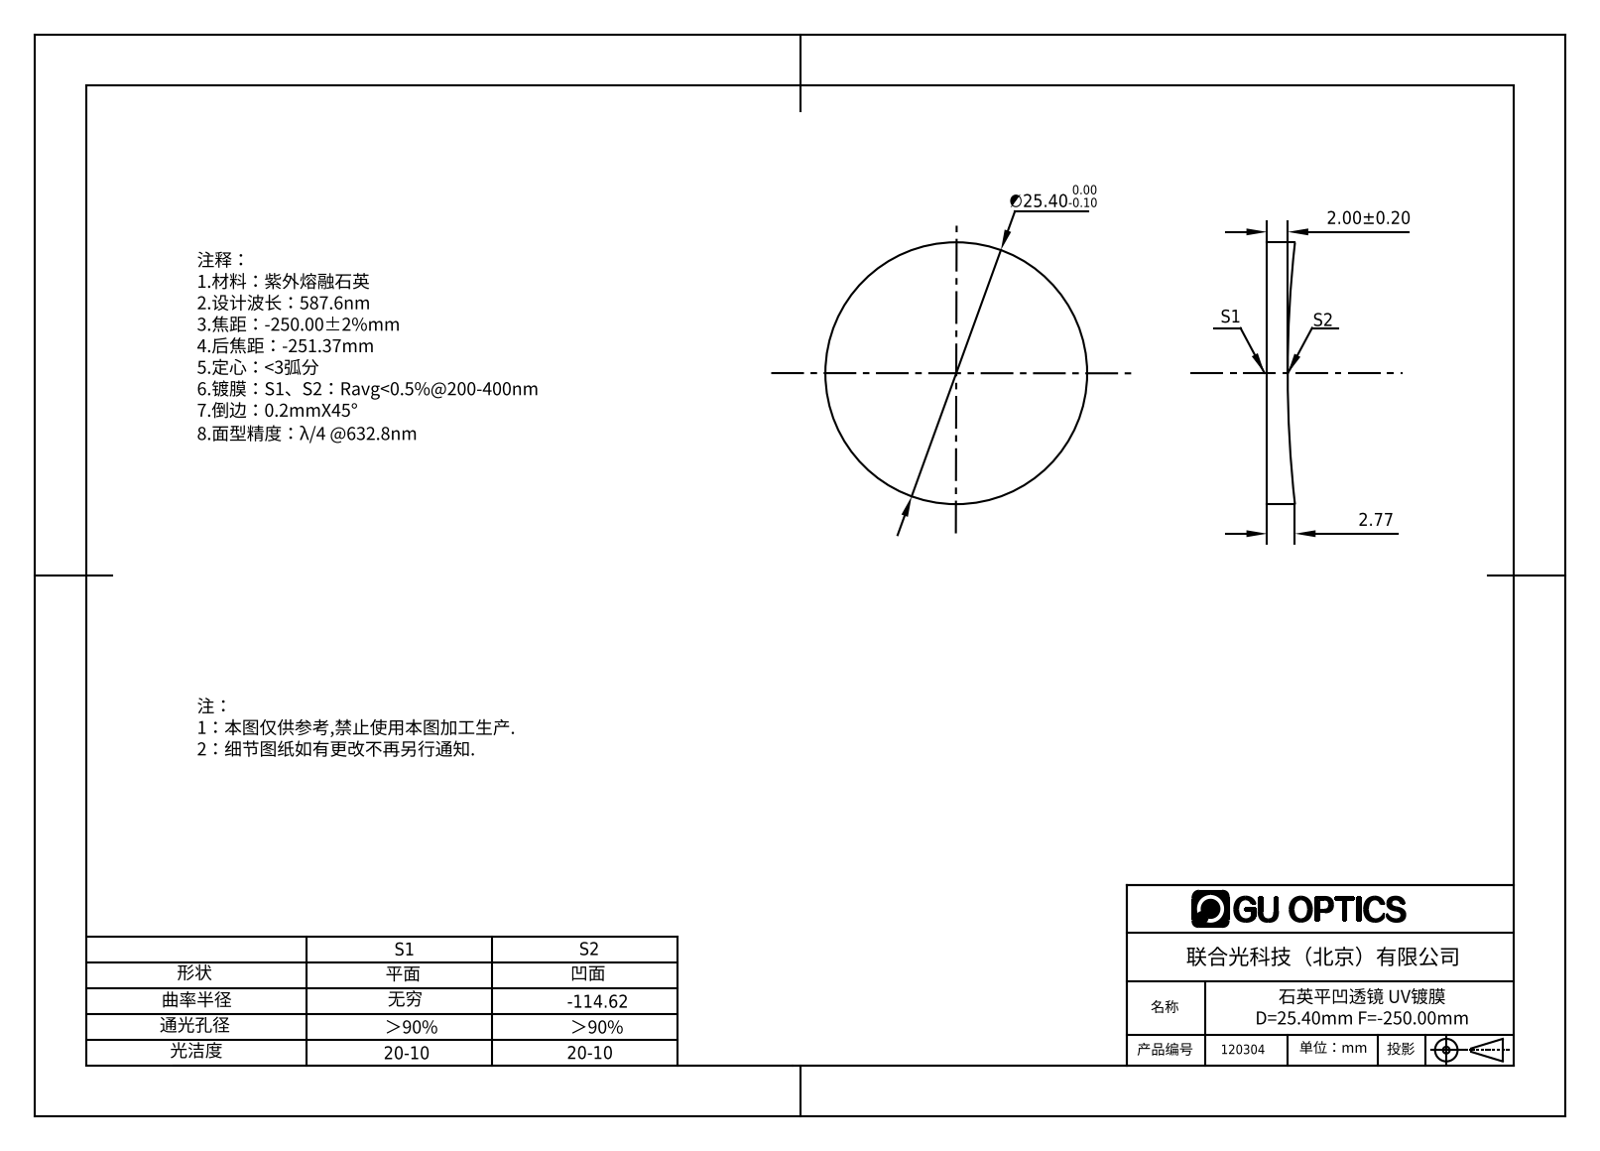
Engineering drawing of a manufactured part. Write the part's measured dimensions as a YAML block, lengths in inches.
part_name: "120271"
step_written_by: "SolidWorks 2016 (AUTOMOTIVE_DESIGN)"
units: inches
bodies: {solids: 1, faces: 5, planar: 1, cylindrical: 2, other: 2}
overall_size: [1, 1, 0.107]
volume: 0.073
surface_area: 1.908
round_bosses_or_shafts:
  - {diameter: 1, count: 1}
